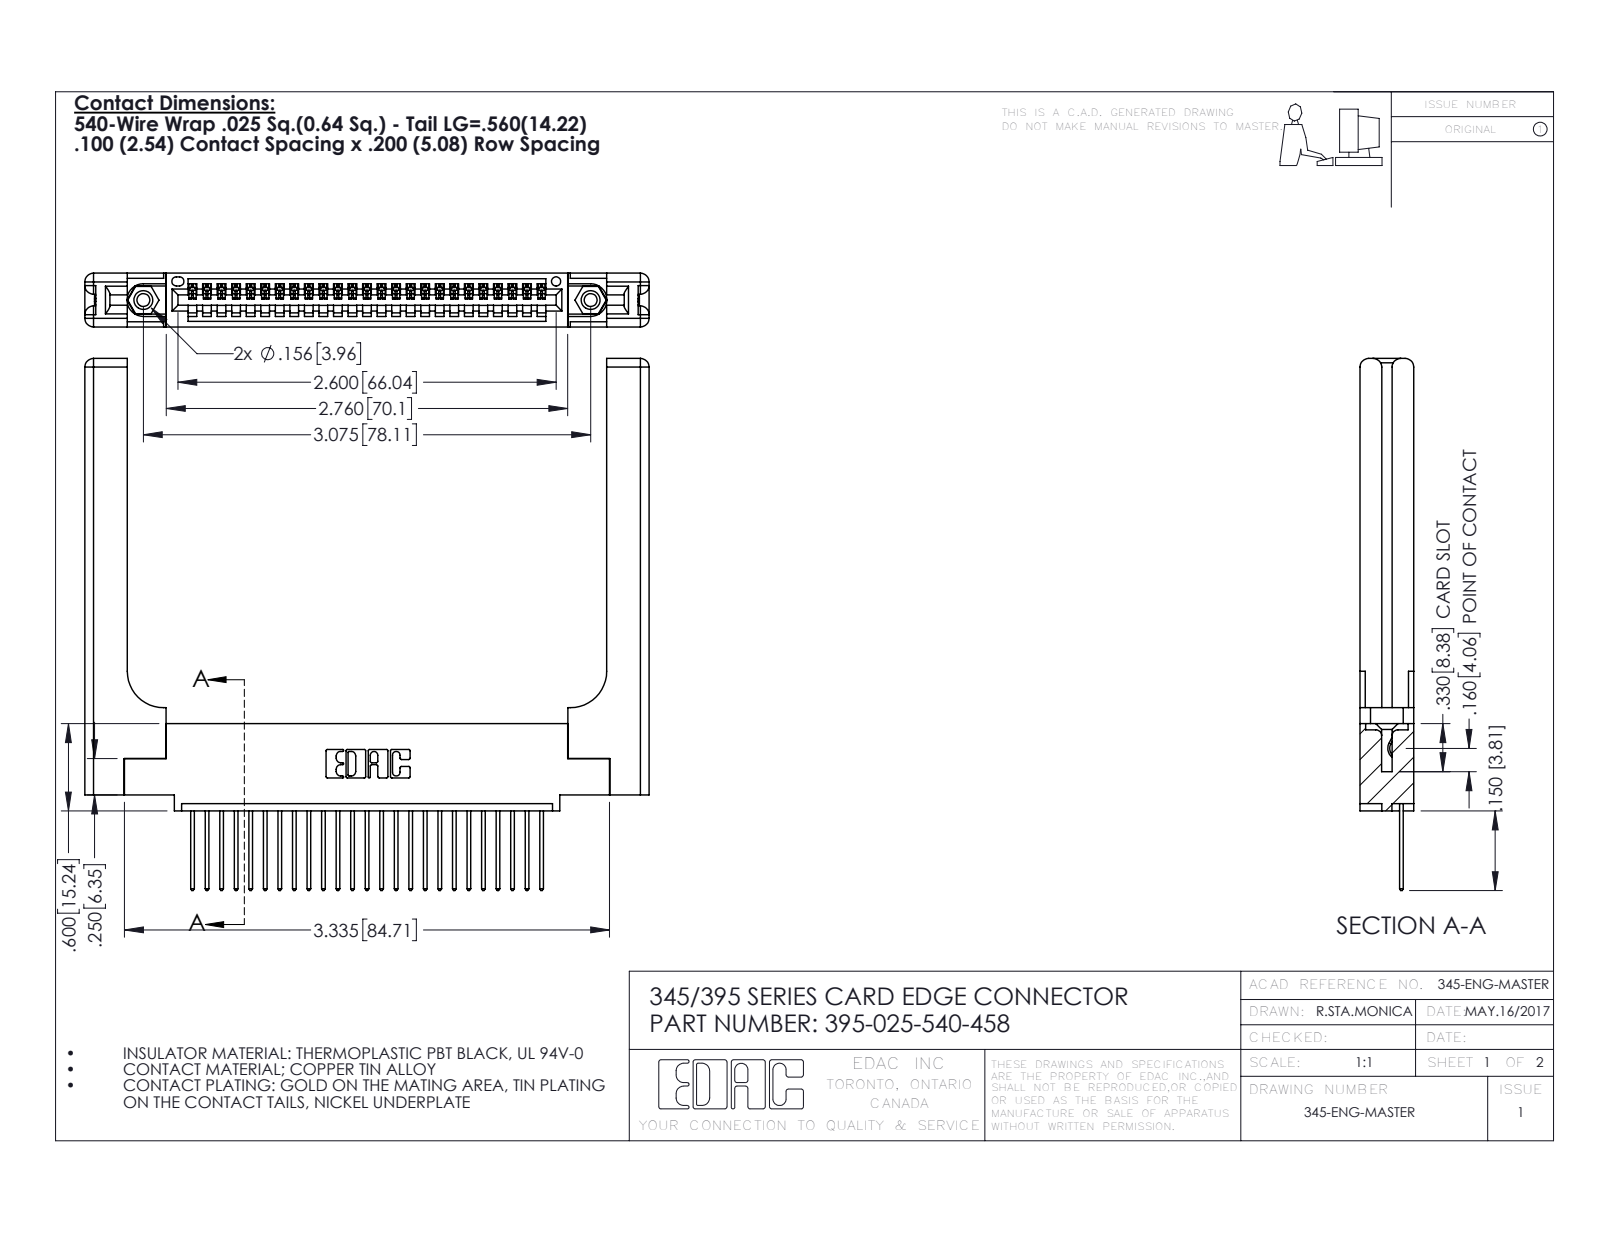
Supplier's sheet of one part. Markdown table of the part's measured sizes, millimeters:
| quantity | value |
| --- | --- |
| part name | 345-220-058_345-220-058; 345 Part_0.110 Offset - 0.156 Dia-TH; 345-292-001_345-293-140; 395-025-540-458 (+1 more) |
| STEP written by | SolidWorks 2016 (CONFIG_CONTROL_DESIGN) |
| units | millimeters |
| bodies | 30 solids, 1836 faces (1232 planar, 544 cylindrical, 60 other) |
| overall size | 98.5 × 92.9 × 9.4 |
| volume | 17 680 mm³ |
| surface area | 17 600 mm² |
| round holes (diameter × count) | 2.3 × 2, 3.2 × 2, 4 × 2, 1.6 × 1 |
| round bosses / shafts (diameter × count) | 3.9 × 2 |
| partial cylindrical surfaces (radius × count) | 0.2 × 50, 0.3 × 50, 0.3 × 22, 1.5 × 16, 0.2 × 6, 0.8 × 6, 0.7 × 3, 0.8 × 2 |
| main face-to-face distances | 9.4, 1.8, 7.6, 2.5, 6.9, 0.6, 3.8, 3.8, 5.1, 2 |
| hole center spacings | 6.9, 72.1, 78.1 |
